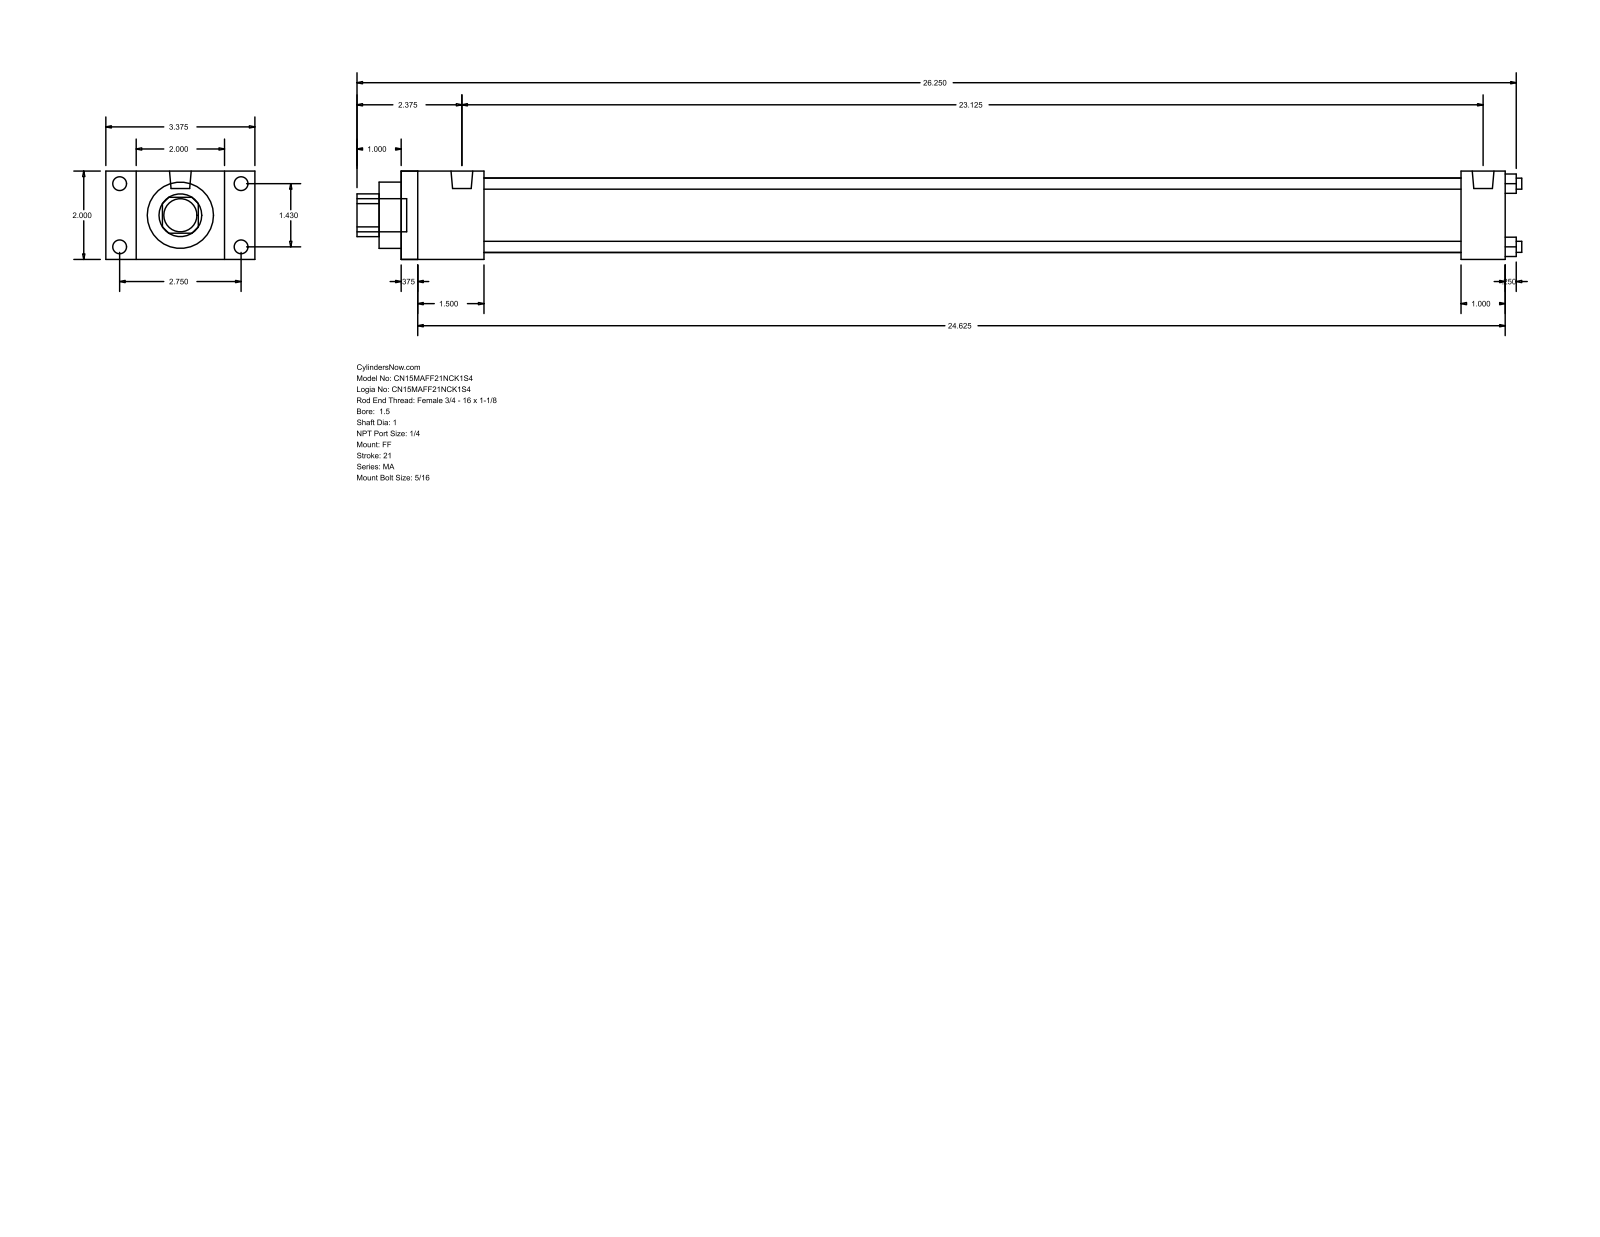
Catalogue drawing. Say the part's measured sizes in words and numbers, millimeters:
The part is named "MA_FF__0150_1". Its 3-D file was written by "GSSL Pune (CONFIG_CONTROL_DESIGN)". It is 0 solids with 92 faces: 64 planar, 28 cylindrical and 0 other. Overall it measures 669.92 by 85.72 by 50.8 millimeters. Round holes: 4 of diameter 6.35, 1 of diameter 25.4, 1 of diameter 38.1, 1 of diameter 42.93. Round bosses or shafts: 8 of diameter 7.94, 2 of diameter 12.49, 1 of diameter 19.05. Partial cylindrical surfaces (rounded edges, fillets, slot ends): 1 of radius 12.29. The main face-to-face distances are 50.8, 635, 9.52, 625.48, 25.4, 47.63, 609.6, 38.11, 600.08, 561.97. The hole center spacings are 25.68, 36.32, 51.36.
